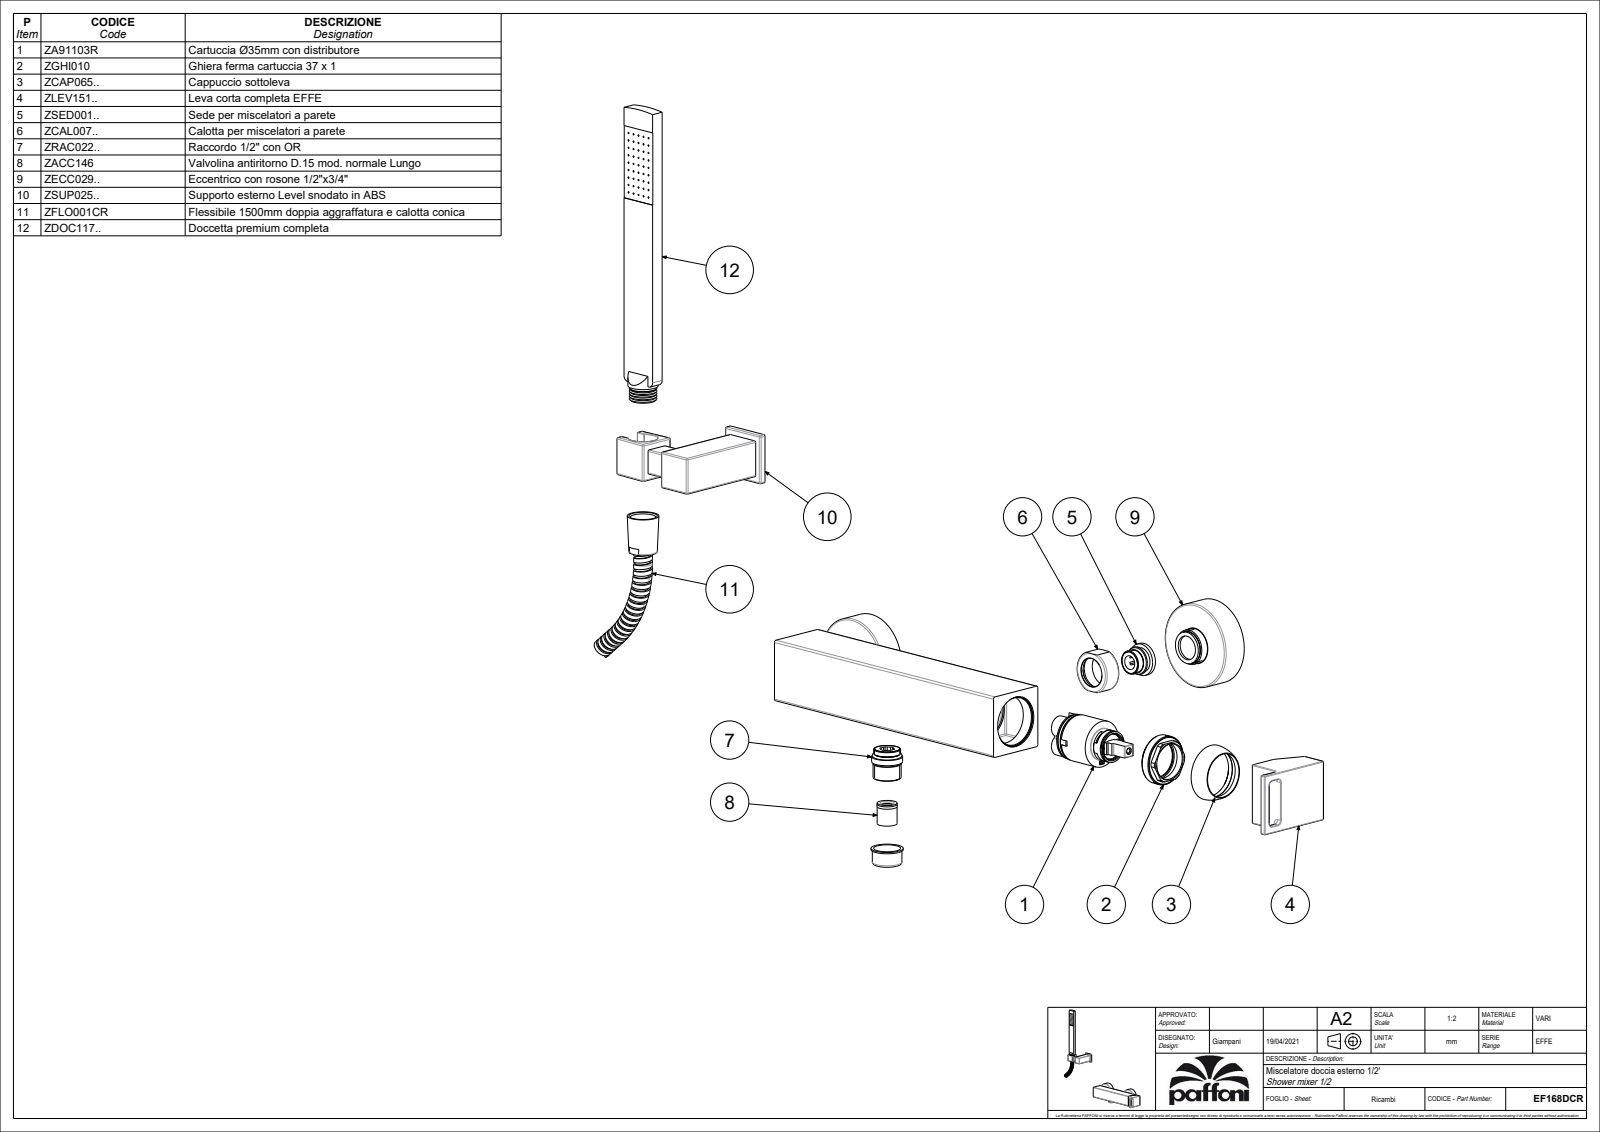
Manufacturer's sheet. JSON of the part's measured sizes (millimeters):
{"part_name": "EF168DCR", "step_written_by": "CREO PARAMETRIC BY PTC INC, 2020044 (CONFIG_CONTROL_DESIGN)", "units": "millimeters", "bodies": {"solids": 2, "faces": 1947, "planar": 1014, "cylindrical": 529, "other": 404}, "overall_size": [475.25, 371, 97.75], "volume_mm3": 409245, "surface_area_mm2": 218407, "round_holes": [[9, 3], [12, 3], [4, 2], [7, 2], [8, 2], [10.5, 2], [18, 2], [21.6, 2], [24.5, 2], [25, 2], [37, 2], [62.3, 2]], "round_bosses_or_shafts": [[2, 11], [63.5, 2], [27, 2], [24, 2], [17.7, 2], [35, 1], [34.8, 1], [33.8, 1]], "partial_cylinders_radius": [[1, 122], [0.5, 66], [0.15, 11], [0.3, 9], [3, 5], [1.5, 4], [7, 4], [4, 3]], "face_to_face_distances": [3.75, 42.75, 46.5, 39, 18.75, 15, 3, 24, 27.75, 42], "hole_center_spacings": [0.71, 8.51, 8.6, 13.04, 13.21, 13.51, 6, 9.5]}
